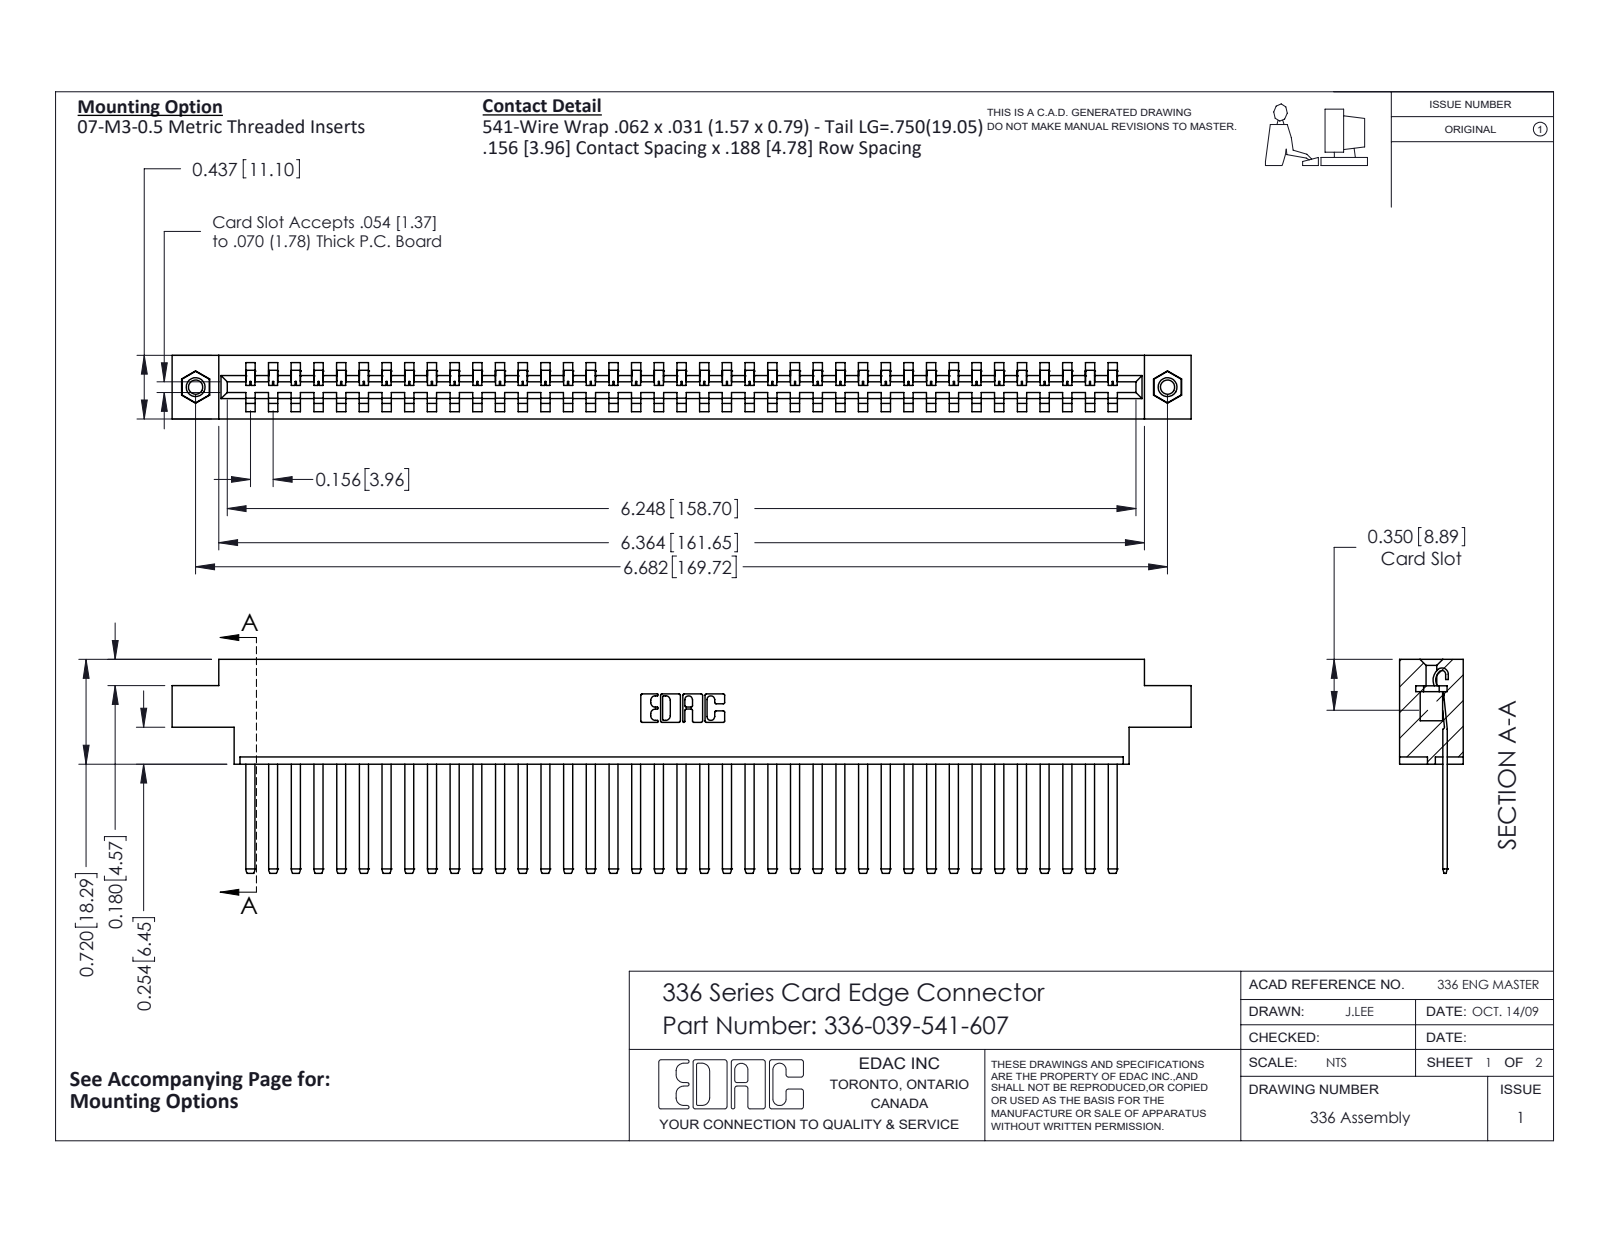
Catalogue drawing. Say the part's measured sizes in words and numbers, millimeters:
The part is named "336-039-541-607; 345-250-001_345-250-005-103; 336 Part_Offset - .156 Dia - TI; 336-290-001_336-290-541". Its 3-D file was written by "SolidWorks 2020 (CONFIG_CONTROL_DESIGN)". It is 42 solids with 2128 faces: 1432 planar, 680 cylindrical and 16 other. Overall it measures 177.9 by 37.3 by 11.1 millimeters. Its volume is 25 830 cubic millimeters and its surface area 28 190 square millimeters. Round holes: 2 of diameter 2.5, 2 of diameter 3.2, 2 of diameter 4. Round bosses or shafts: 2 of diameter 3.9. Partial cylindrical surfaces (rounded edges, fillets, slot ends): 78 of radius 0.1, 78 of radius 1.4, 22 of radius 0.3, 6 of radius 0.2, 6 of radius 0.8, 3 of radius 0.7, 2 of radius 0.6, 2 of radius 1. The main face-to-face distances are 11.1, 4.6, 8.3, 3.6, 7.5, 2.8, 0.8, 6.5, 1.3, 3.3. The hole center spacings are 169.7.
